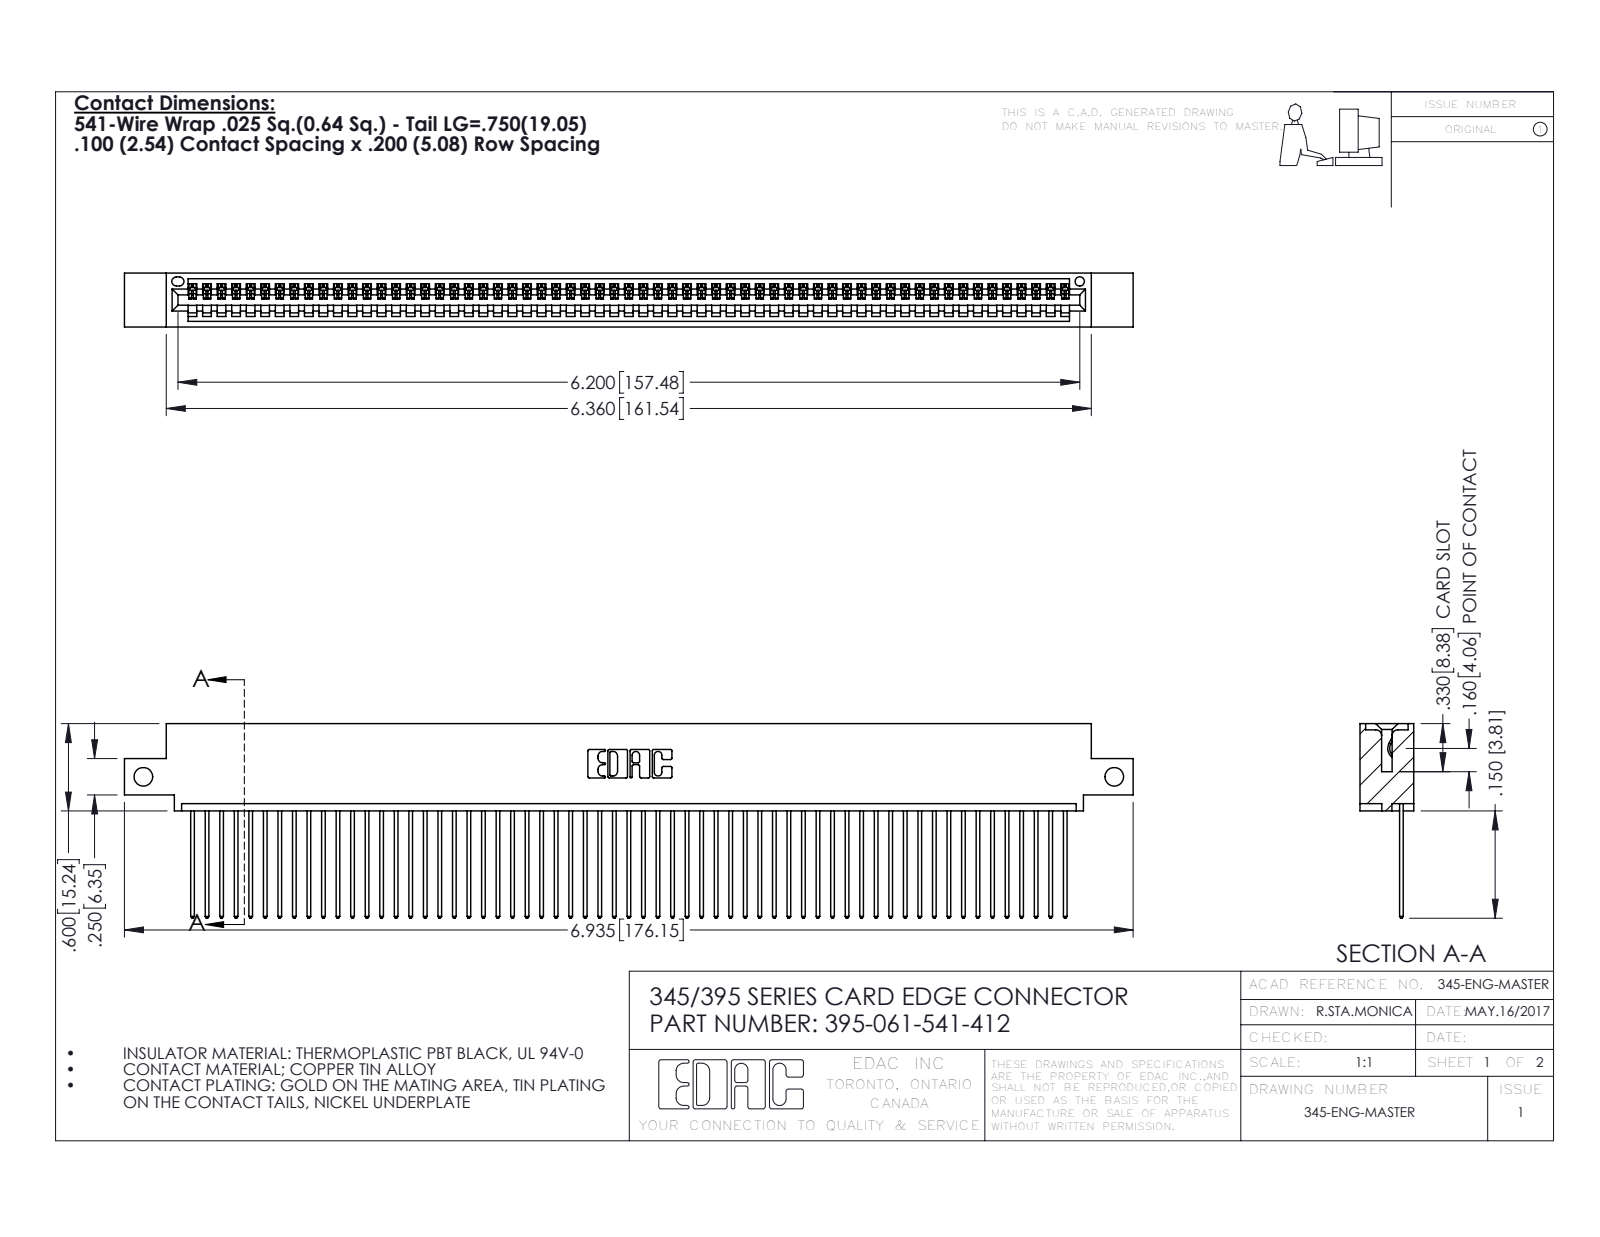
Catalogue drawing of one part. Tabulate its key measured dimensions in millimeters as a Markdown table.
| quantity | value |
| --- | --- |
| part name | 345-292-001_345-293-141; 345 Part_0.110 Offset - Side Mount; 395-061-541-412 |
| STEP written by | SolidWorks 2016 (CONFIG_CONTROL_DESIGN) |
| units | millimeters |
| bodies | 62 solids, 3668 faces (2524 planar, 1144 cylindrical, 0 other) |
| overall size | 176.1 × 34 × 9.4 |
| volume | 16 930 mm³ |
| surface area | 23 880 mm² |
| round holes (diameter × count) | 3.3 × 2, 1.6 × 1 |
| partial cylindrical surfaces (radius × count) | 0.2 × 122, 0.3 × 122, 0.3 × 22, 0.2 × 6, 0.8 × 6, 0.7 × 3, 0.8 × 2, 1 × 2 |
| main face-to-face distances | 1.8, 7.6, 2.5, 6.9, 0.6, 9.4, 5.1, 5.7, 3.8, 1.8 |
| hole center spacings | 169.5 |
